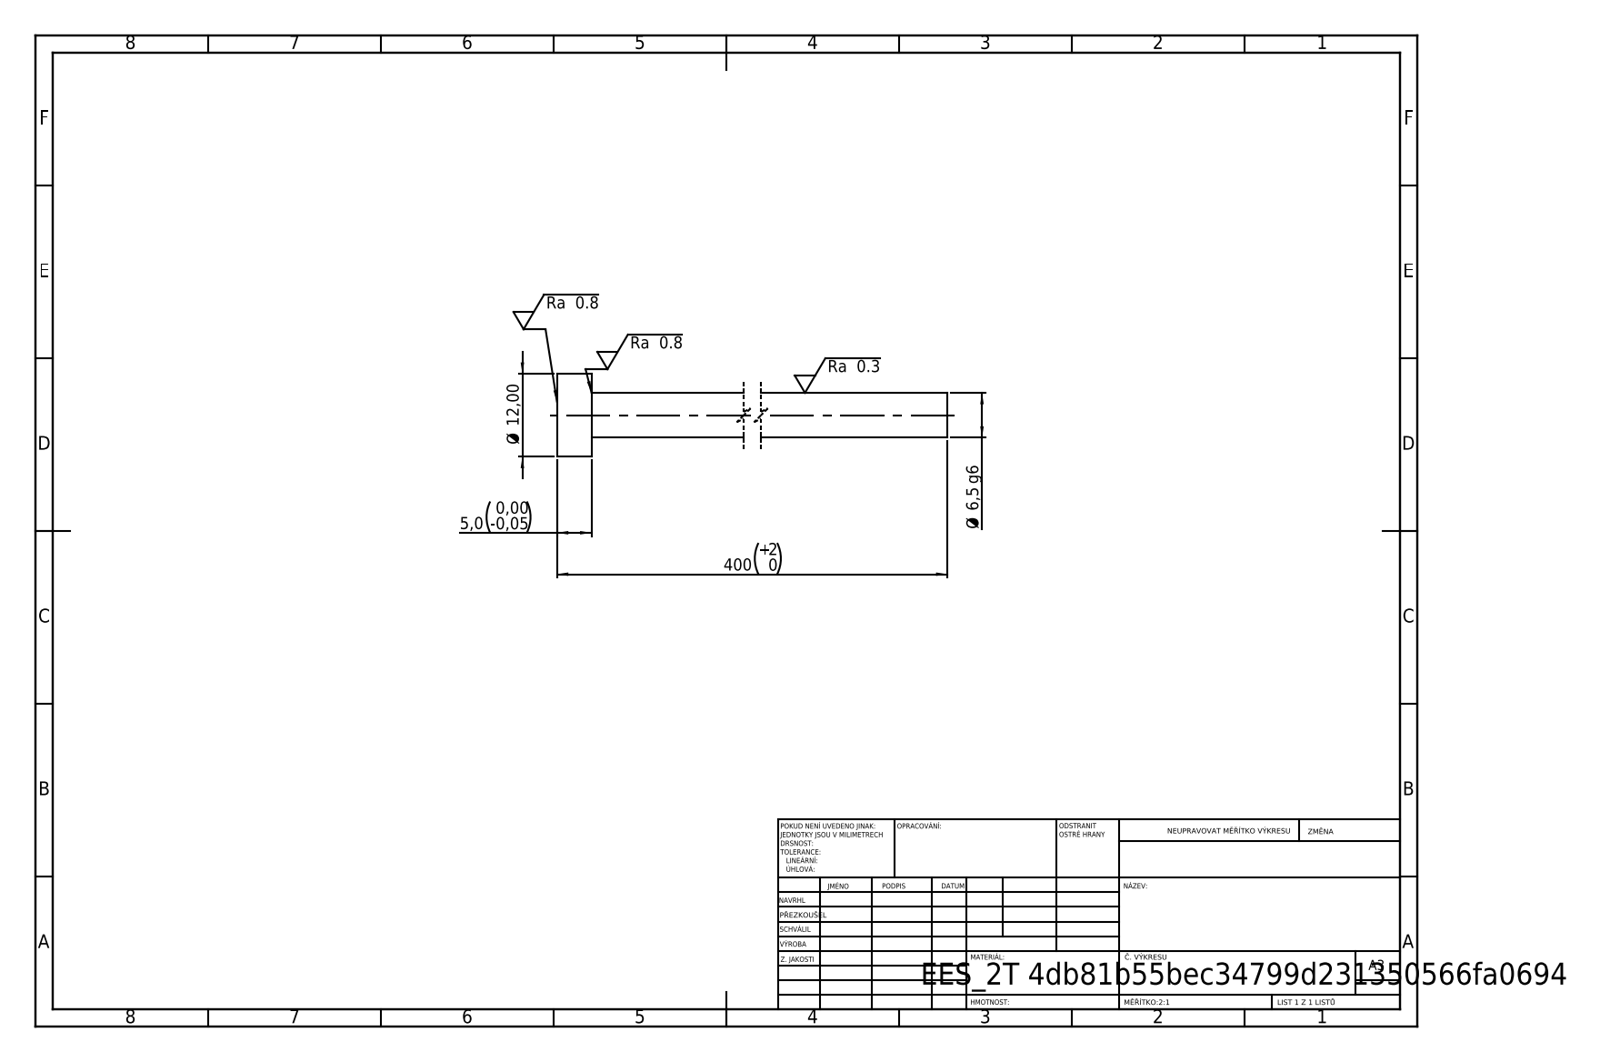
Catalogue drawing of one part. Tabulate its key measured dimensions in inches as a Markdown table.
| quantity | value |
| --- | --- |
| STEP written by | SolidWorks 2019 (CONFIG_CONTROL_DESIGN) |
| units | inches |
| bodies | 1 solid, 7 faces (3 planar, 4 cylindrical, 0 other) |
| overall size | 15.748 × 0.472 × 0.472 |
| volume | 0.834 in³ |
| surface area | 13.15 in² |
| round bosses / shafts (diameter × count) | 0.472 × 1, 0.256 × 1 |
| main face-to-face distances | 0.197, 15.748, 15.551 |
